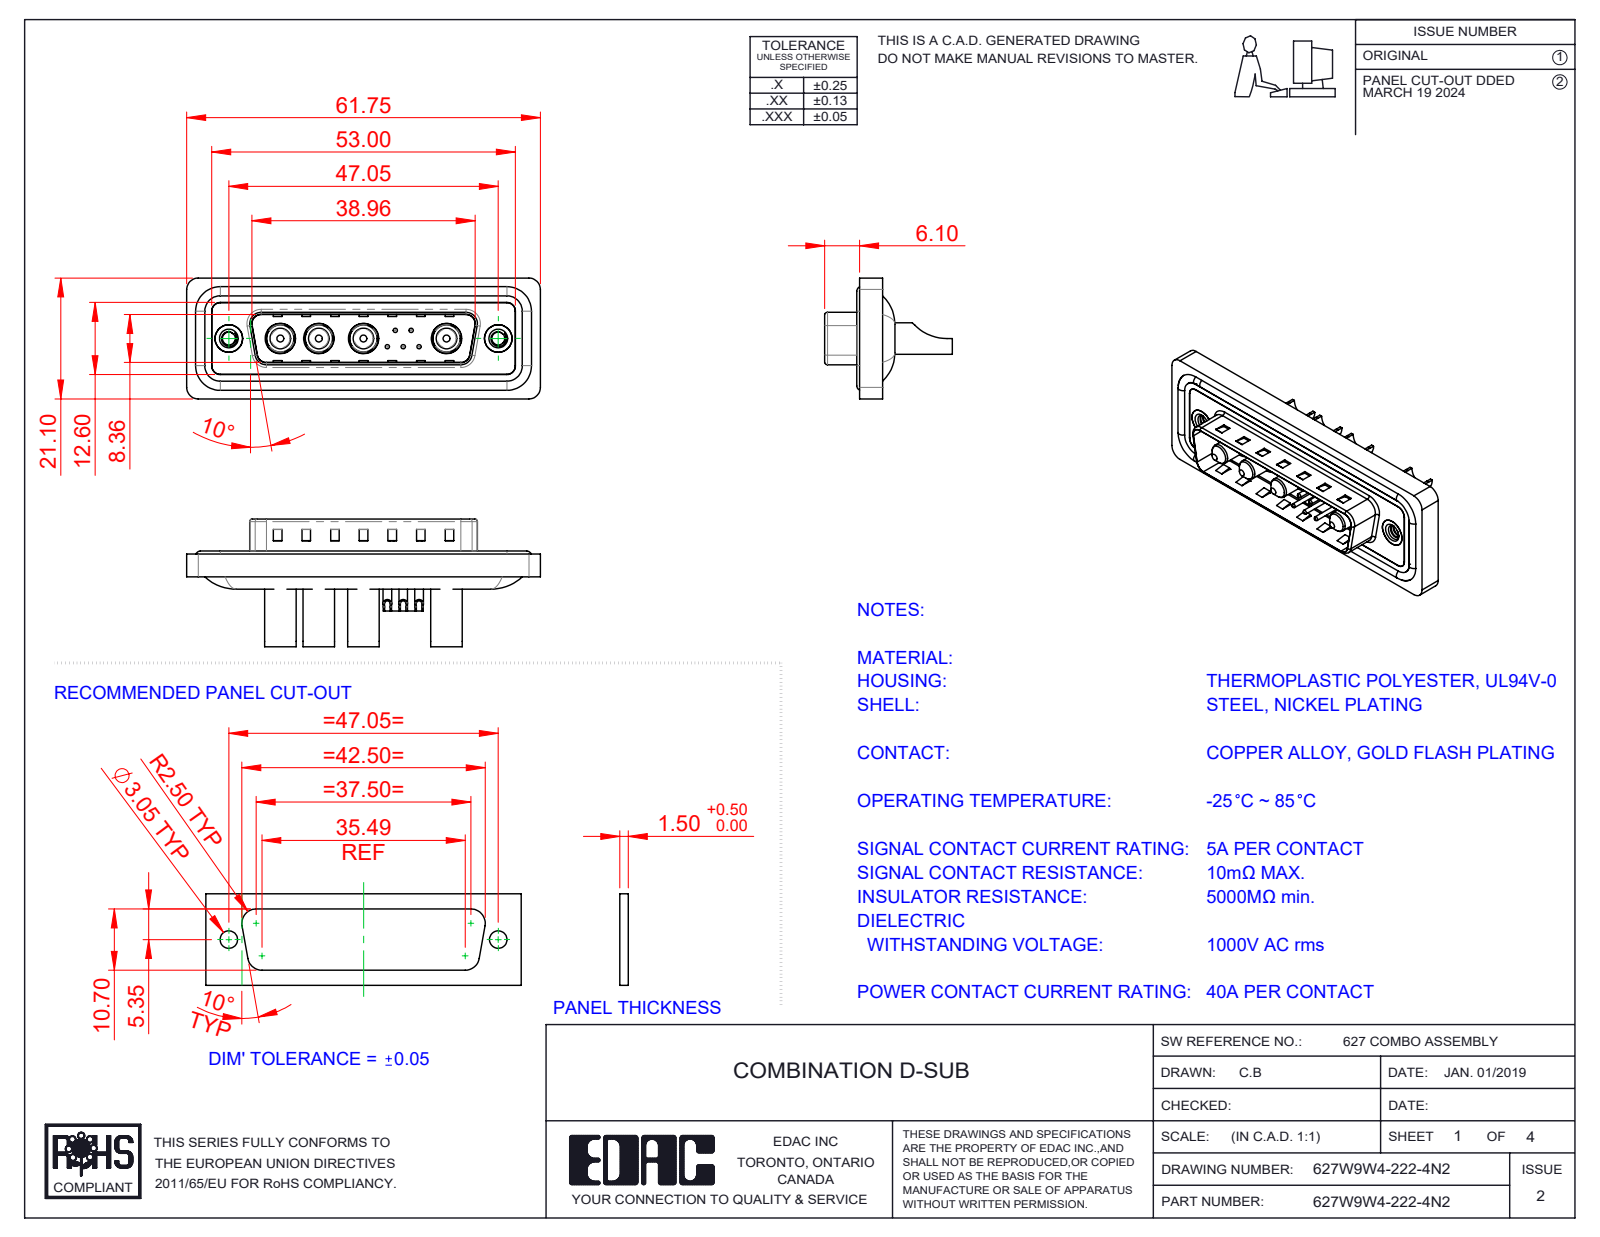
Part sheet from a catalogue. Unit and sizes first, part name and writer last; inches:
Units: inches
Overall size (bounding box): 2.431 × 0.878 × 0.831
Round holes (diameter × count): ⌀0.03 ×5, ⌀0.039 ×5, ⌀0.063 ×5, ⌀0.079 ×5, ⌀0.181 ×4, ⌀0.191 ×4, ⌀0.209 ×4, ⌀0.089 ×2, ⌀0.157 ×2, ⌀0.189 ×2, ⌀0.197 ×2
Round bosses / shafts (diameter × count): ⌀0.059 ×5, ⌀0.217 ×4, ⌀0.205 ×4, ⌀0.187 ×4, ⌀0.148 ×4, ⌀0.142 ×4, ⌀0.063 ×4, ⌀0.193 ×2
Partial cylindrical surfaces — rounded edges, fillets, slot ends (radius × count): R0.059 ×22, R0.079 ×18, R0.02 ×8, R0.063 ×8, R0.039 ×6, R0.01 ×4, R0.024 ×4, R0.026 ×4
Main face-to-face distances: 0.016, 0.043, 0.059, 0.02, 0.063, 0.122, 0.114, 0.032, 0.377, 0.222
Hole centre spacings: 0.124, 0.109, 0.198, 0.571, 0.109, 0.173, 0.174, 0.197
Volume: 0.462 in³ · Surface area: 19.27 in²
Bodies: 20 solids, 840 faces (302 planar, 348 cylindrical, 190 other)
Part name (STEP PRODUCT): 627Combo Housing_9W4; 627Combo Contact Row 1_22; 627W9W4-222-4N2; 627Combo Threaded Rivet_2 (+5 more)
STEP written by: SolidWorks 2023 (CONFIG_CONTROL_DESIGN)
